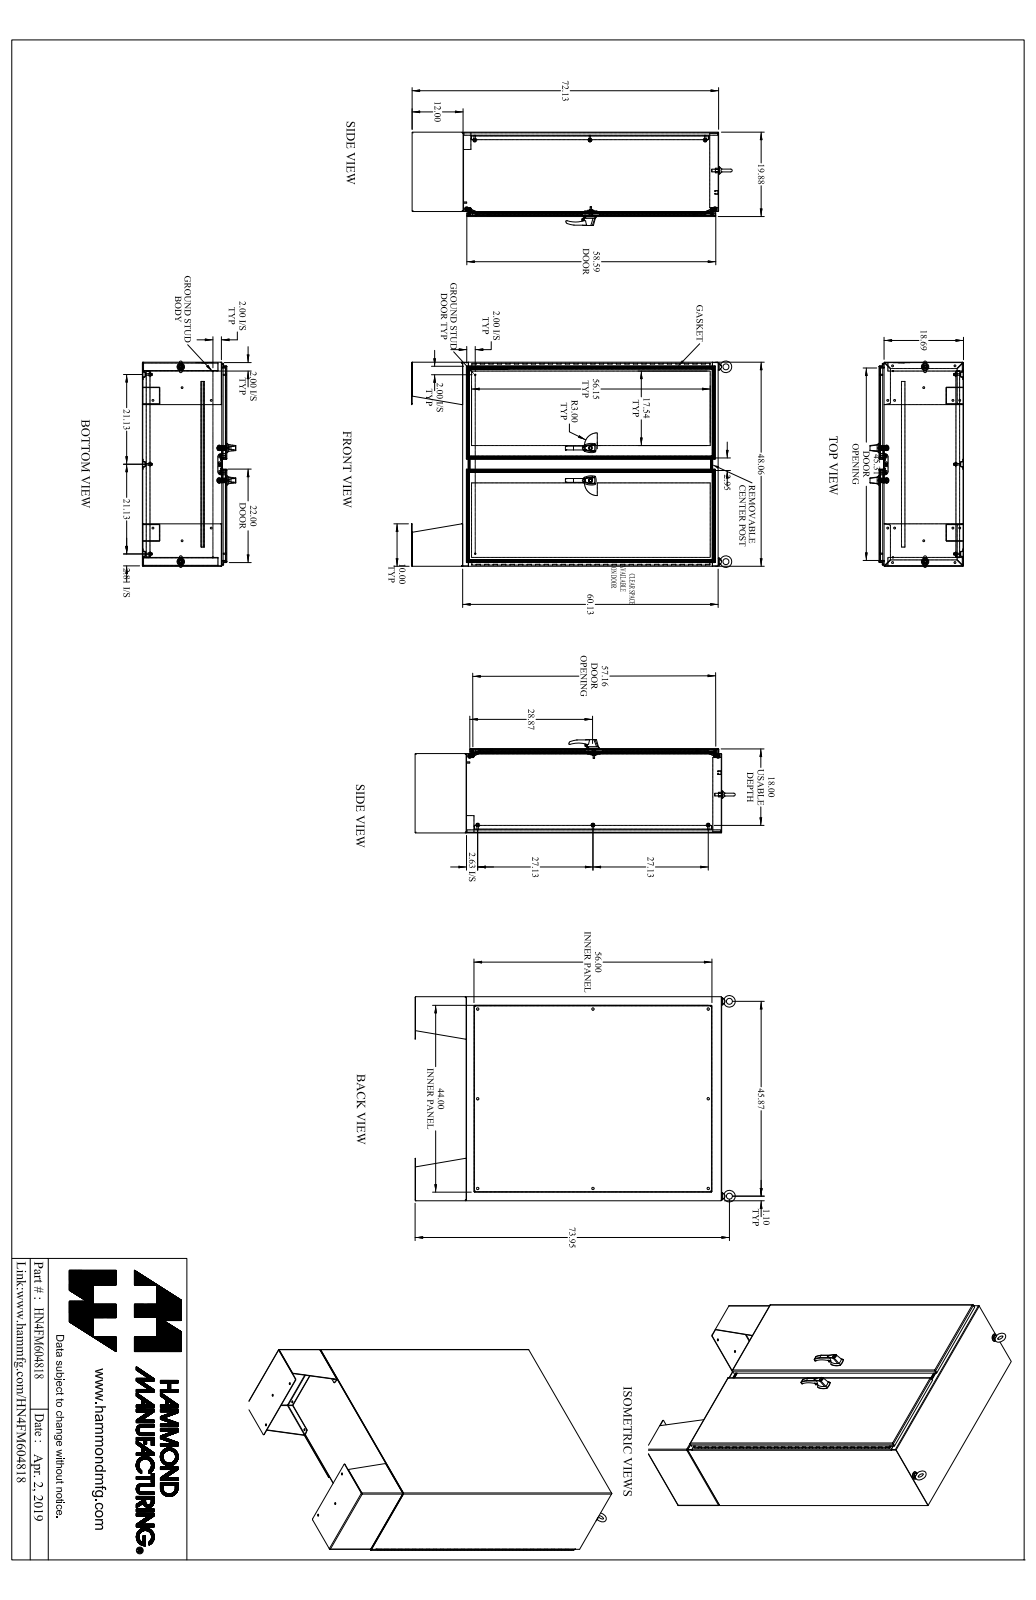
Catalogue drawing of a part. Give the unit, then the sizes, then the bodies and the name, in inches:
Units: inches
Overall size (bounding box): 75.315 × 48.606 × 21.99
Round holes (diameter × count): ⌀0.304 ×20, ⌀0.437 ×14, ⌀0.307 ×8, ⌀0.35 ×8, ⌀0.563 ×8, ⌀0.25 ×6, ⌀0.445 ×6, ⌀0.281 ×4, ⌀0.313 ×4, ⌀0.39 ×4, ⌀0.201 ×3, ⌀0.313 ×3
Round bosses / shafts (diameter × count): ⌀1 ×10, ⌀0.65 ×8, ⌀0.375 ×8, ⌀0.33 ×8, ⌀0.281 ×8, ⌀0.75 ×4, ⌀0.625 ×4, ⌀0.44 ×4
Partial cylindrical surfaces — rounded edges, fillets, slot ends (radius × count): R0.5 ×33, R0.018 ×32, R0.125 ×32, R0.06 ×28, R0.048 ×27, R0.143 ×27, R0.03 ×12, R0.09 ×12
Main face-to-face distances: 0.095, 19.78, 19.685, 17.998, 47.967, 0.125, 19.875, 1.782, 1.687, 18.093
Hole centre spacings: 6, 12, 18, 24, 30, 46.593, 1.61, 8.139
Volume: 1 658 in³ · Surface area: 33 390 in²
Bodies: 130 solids, 3768 faces (1736 planar, 1659 cylindrical, 373 other)
Part name (STEP PRODUCT): HN4FM604818
STEP written by: SolidWorks 2018 (AUTOMOTIVE_DESIGN)
